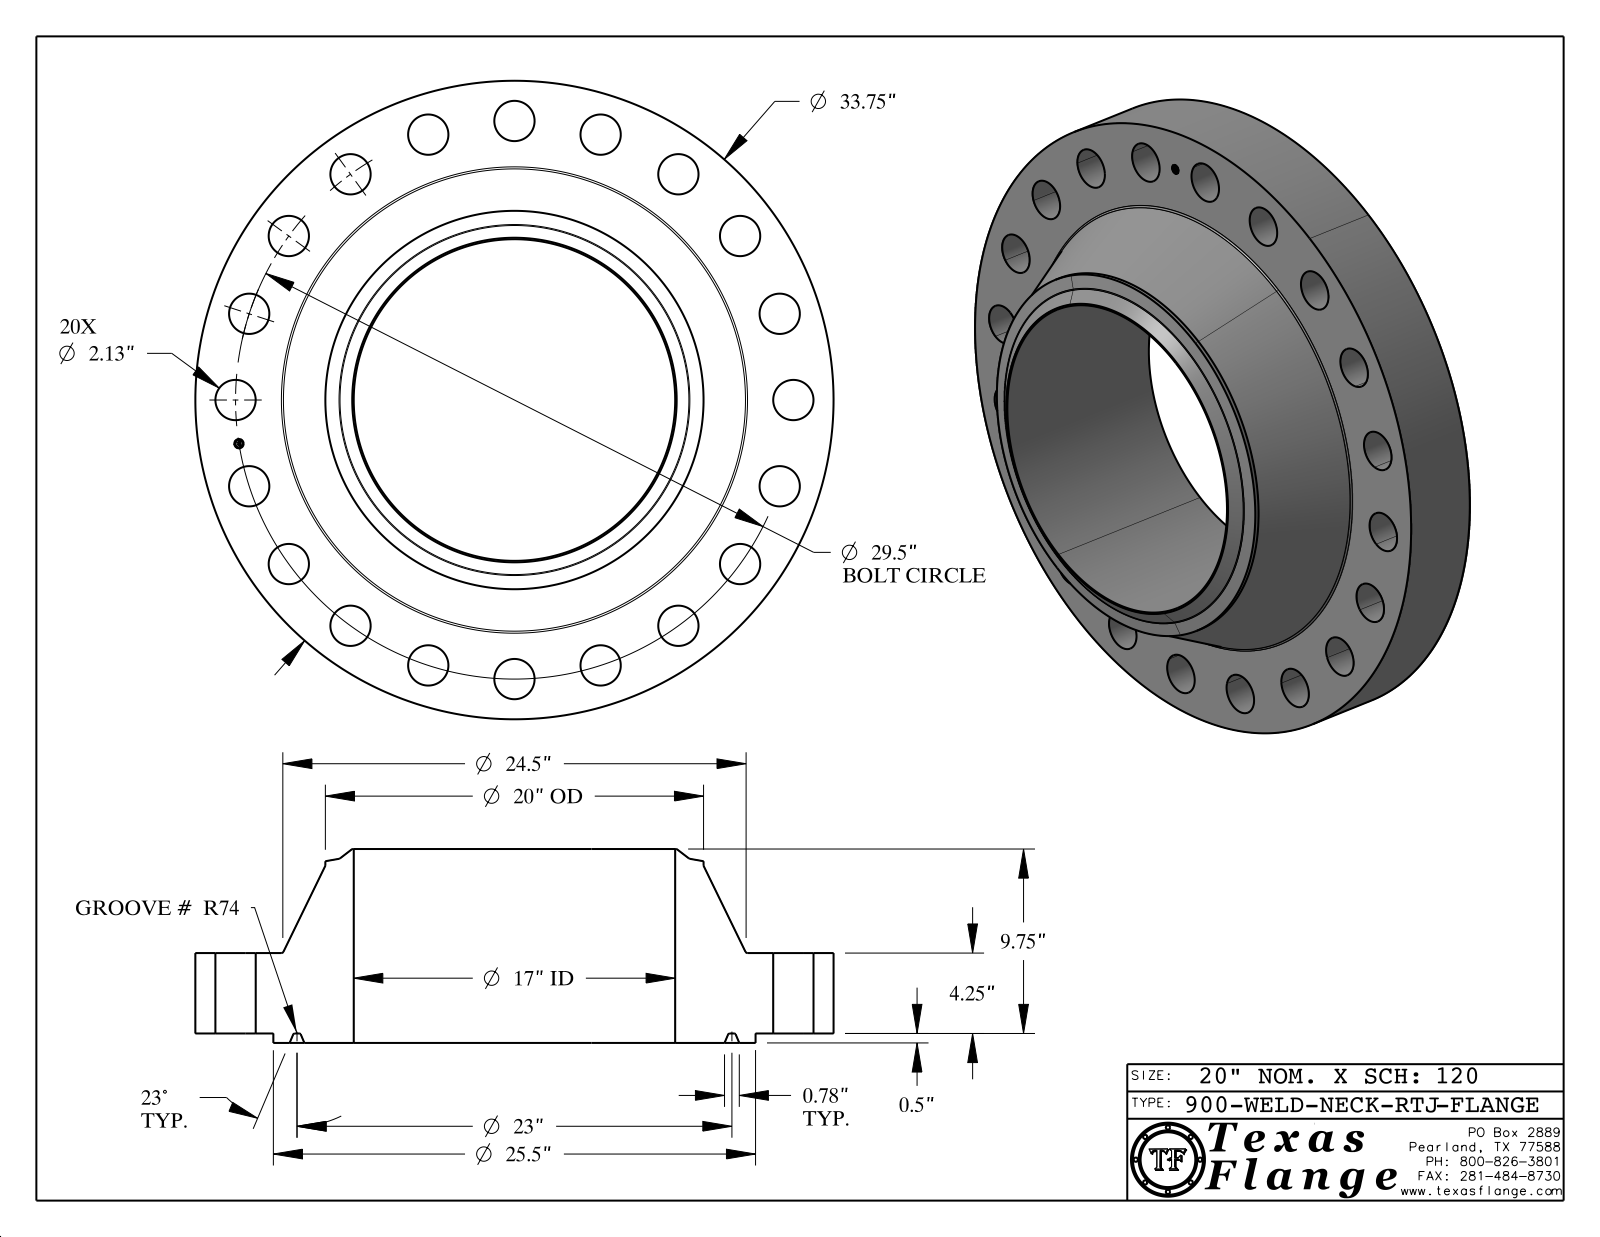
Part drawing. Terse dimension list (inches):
name: 900-WELD-NECK-RTJ
written by: CATIA V5 STEP AP214 (AUTOMOTIVE_DESIGN)
unit: in
bodies: 1 solid, 457 faces (371 planar, 68 cylindrical, 18 other)
size: 33.75 × 33.75 × 10.25
volume: 3 450 in³; area: 3 072 in²
holes: 20× ⌀2.13, 1× ⌀0.495, 1× ⌀17
bosses: 8× ⌀0.03, 1× ⌀33.75, 1× ⌀25.5, 1× ⌀20, 1× ⌀0.39
face distances: 4.25, 0.5, 4.75, 10.25, 9.75, 5.5, 4.735, 4.235, 0.015, 5.515
hole spacings: 14.75, 29.137, 4.615, 17.34, 20.859, 23.866, 26.285, 9.116
